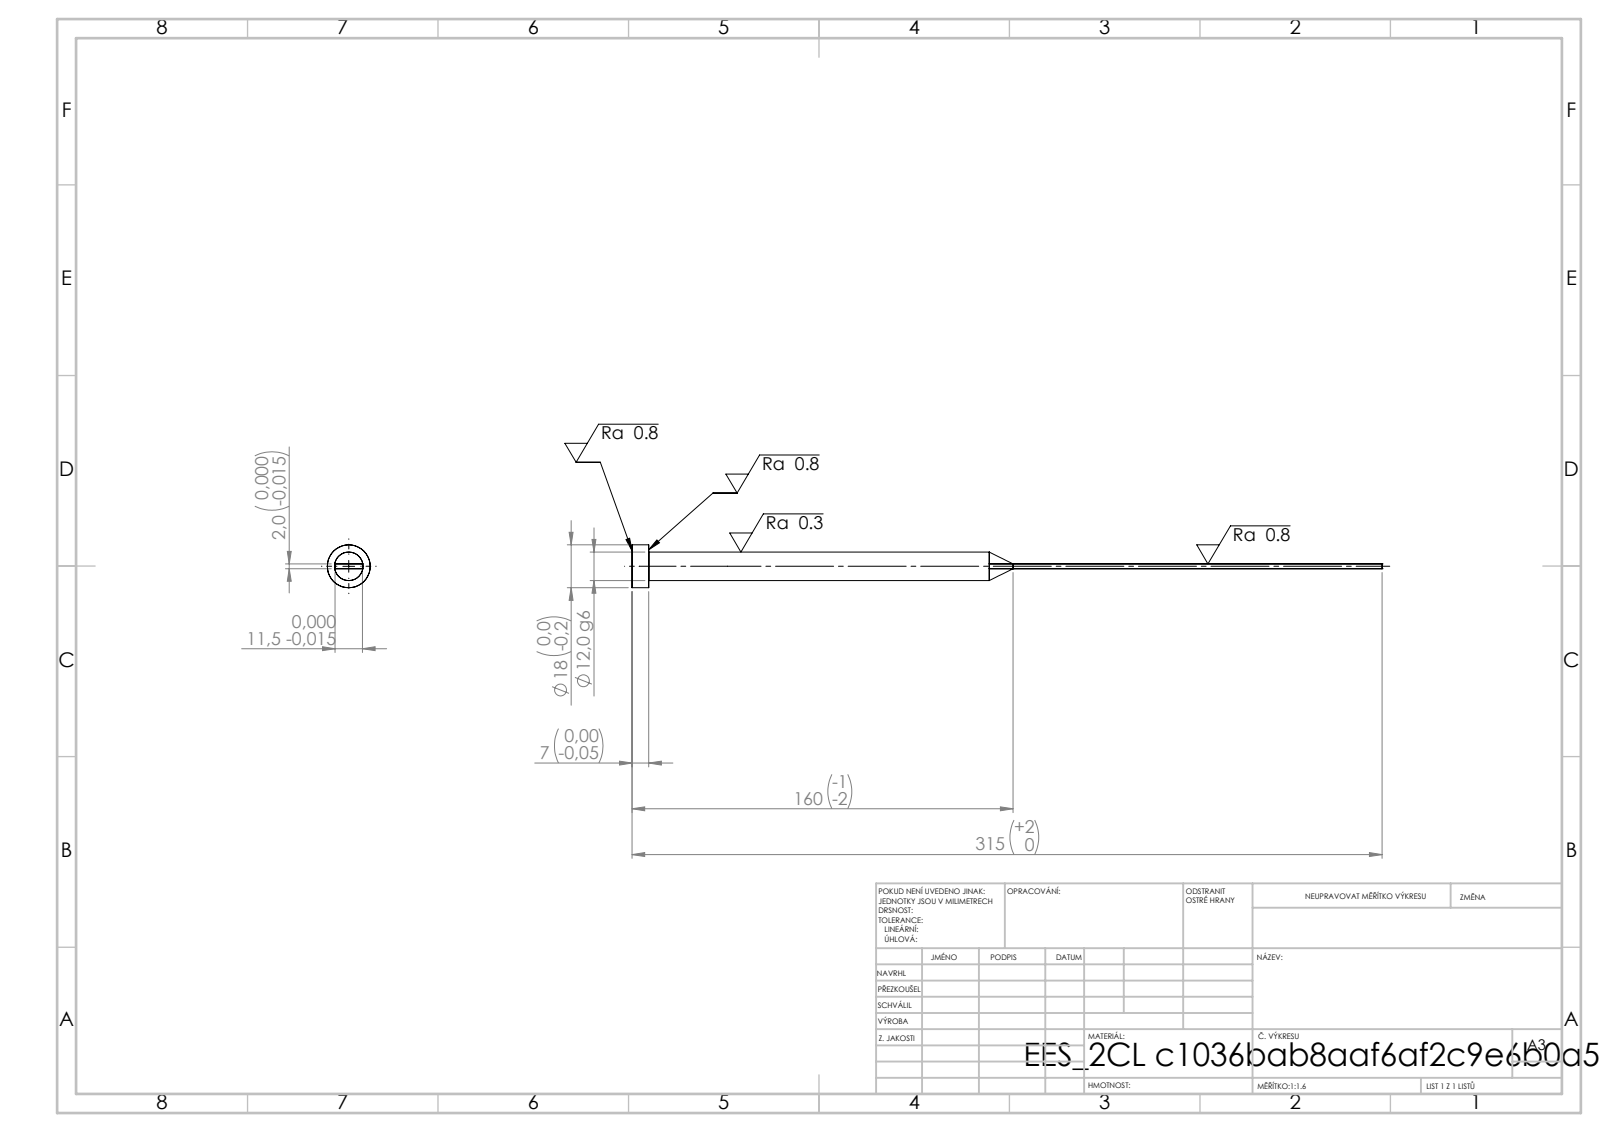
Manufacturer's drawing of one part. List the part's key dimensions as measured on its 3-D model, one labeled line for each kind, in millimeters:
STEP written by: SolidWorks 2019 (CONFIG_CONTROL_DESIGN)
Units: millimetres
Bodies: 1 solid, 15 faces (7 planar, 4 cylindrical, 4 other)
Overall size (bounding box): 315 × 18 × 18
Volume: 22 165 mm³ · Surface area: 10 716 mm²
Round bosses / shafts (diameter × count): ⌀18 ×1, ⌀12 ×1
Main face-to-face distances: 2, 11.5, 7, 315, 308
